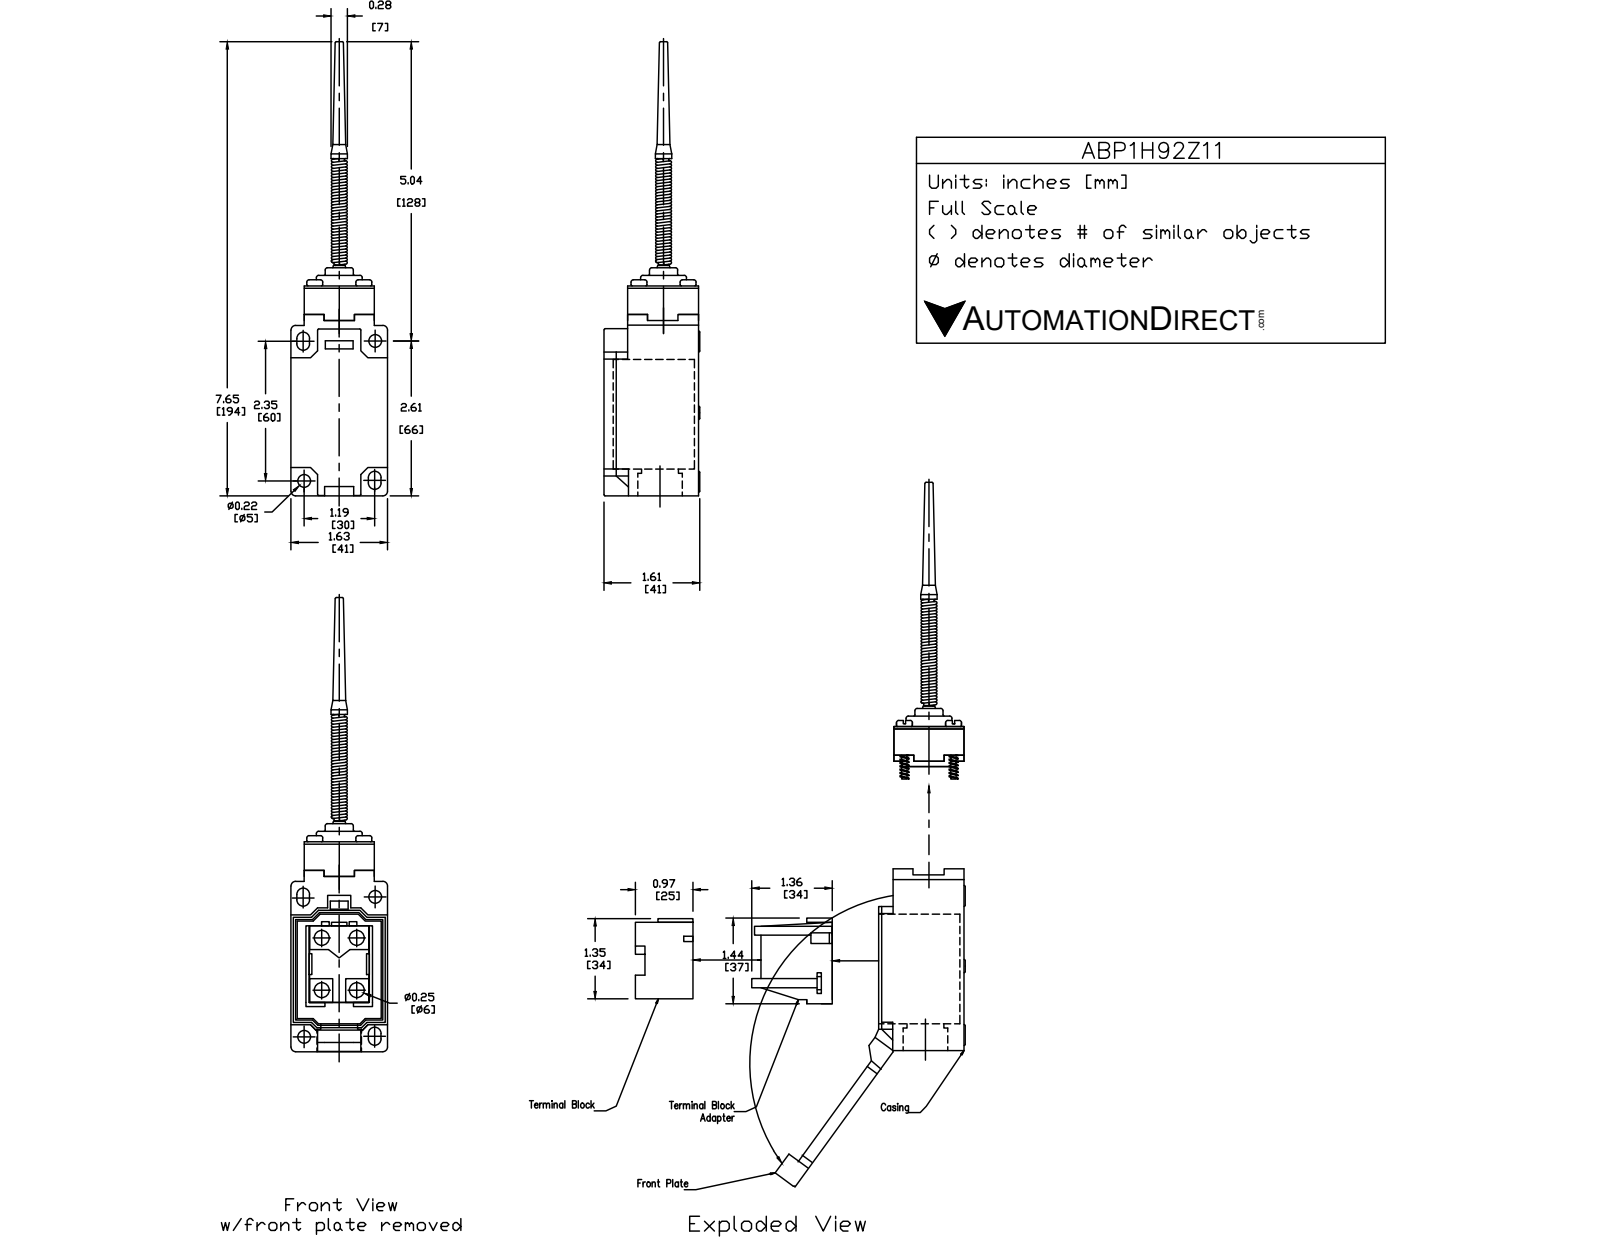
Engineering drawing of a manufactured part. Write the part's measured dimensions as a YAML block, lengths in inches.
part_name: "ABP1H92Z11"
step_written_by: "SolidWorks 2017 (AUTOMOTIVE_DESIGN)"
units: inches
bodies: {solids: 3, faces: 193, planar: 81, cylindrical: 76, other: 36}
overall_size: [7.618, 1.614, 1.585]
volume: 7.762
surface_area: 37.44
round_holes:
  - {diameter: 0.213, count: 2}
  - {diameter: 0.669, count: 1}
  - {diameter: 0.748, count: 1}
  - {diameter: 0.807, count: 1}
round_bosses_or_shafts:
  - {diameter: 0.354, count: 4}
  - {diameter: 0.276, count: 4}
  - {diameter: 0.748, count: 1}
  - {diameter: 0.461, count: 1}
  - {diameter: 0.268, count: 1}
partial_cylinders:
  - {radius: 0.02, count: 16}
  - {radius: 0.024, count: 4}
  - {radius: 0.079, count: 4}
  - {radius: 0.106, count: 4}
  - {radius: 0.453, count: 1}
  - {radius: 0.472, count: 1}
face_to_face_distances: [1.614, 1.565, 1.181, 2.972, 1.398, 0.384, 0.217, 3.071, 0.098, 2.598]
hole_center_spacings: [0.059, 2.641]
